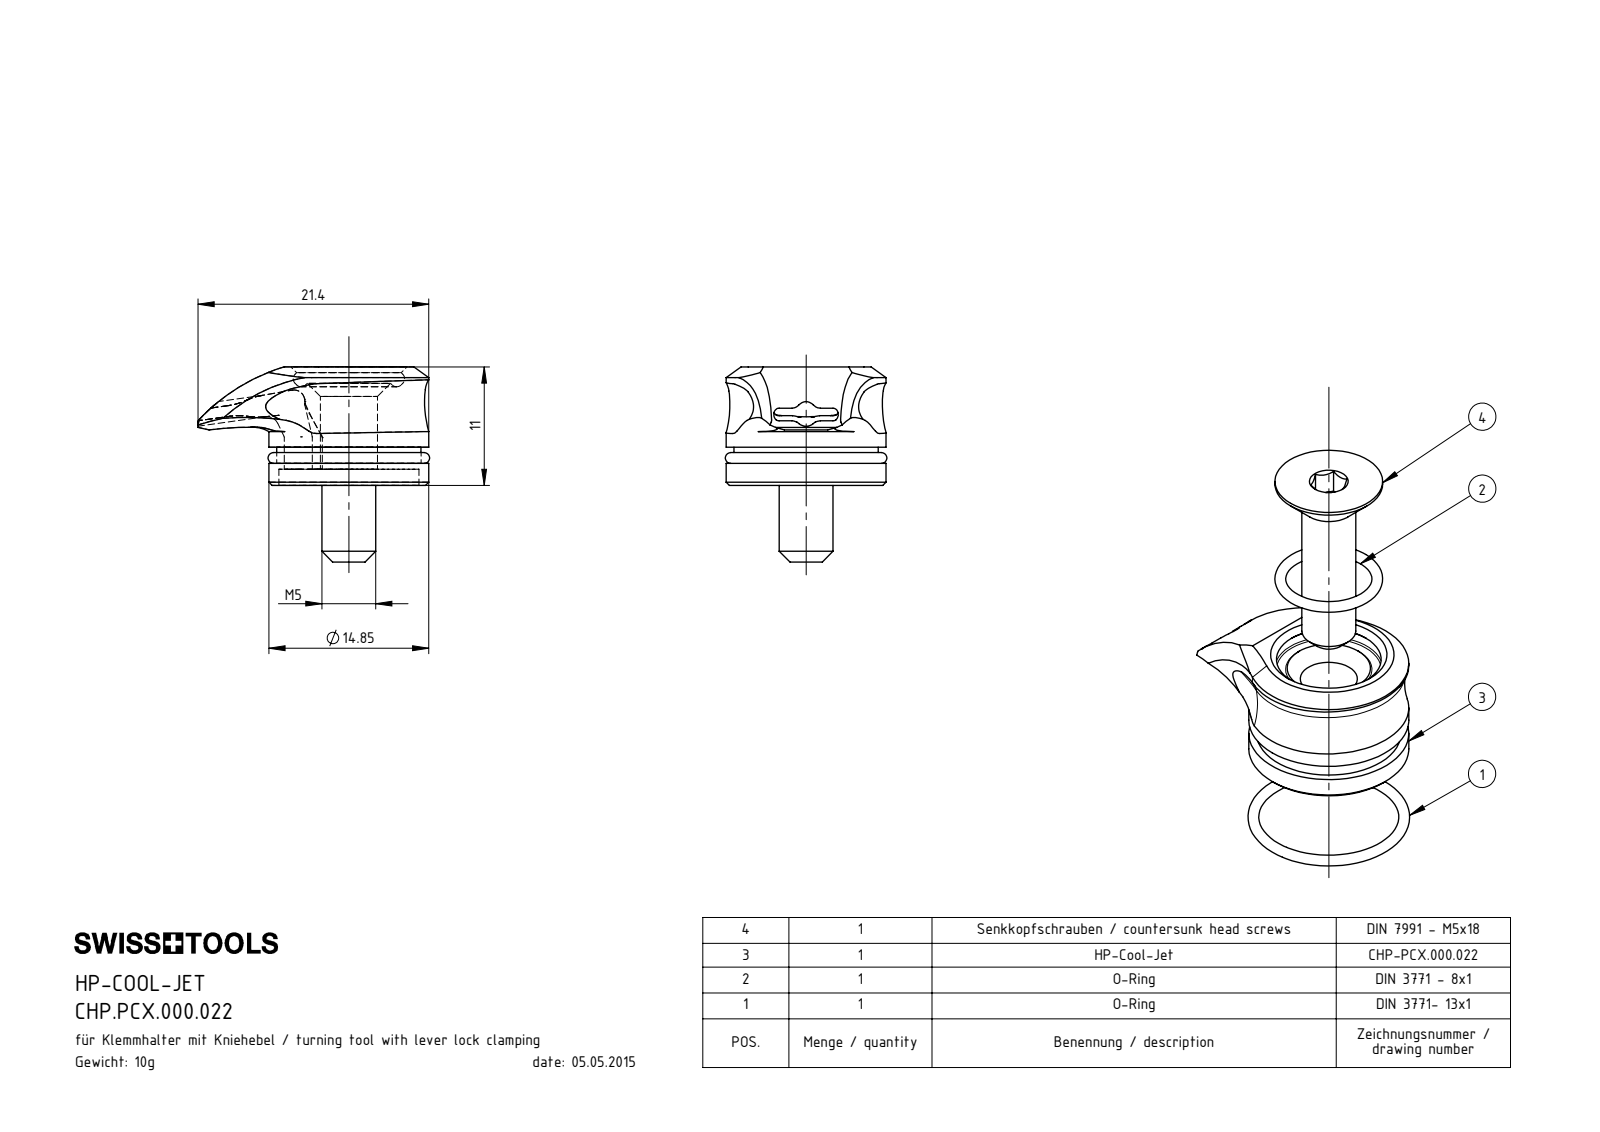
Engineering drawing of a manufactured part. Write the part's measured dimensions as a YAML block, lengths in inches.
part_name: "CHP-PCX.000.022_B; DIN 7991 - M5x18; DIN 3771 - 6.5x1.5; DIN 3771 - 13x1 (+1 more)"
step_written_by: "SolidWorks 2017 (AUTOMOTIVE_DESIGN)"
units: inches
bodies: {solids: 4, faces: 138, planar: 30, cylindrical: 38, other: 70}
overall_size: [0.846, 0.713, 0.591]
volume: 0.108
surface_area: 3.264
round_holes:
  - {diameter: 0.209, count: 1}
  - {diameter: 0.512, count: 1}
round_bosses_or_shafts:
  - {diameter: 0.585, count: 1}
  - {diameter: 0.528, count: 1}
  - {diameter: 0.394, count: 1}
  - {diameter: 0.197, count: 1}
partial_cylinders:
  - {radius: 0.039, count: 7}
  - {radius: 0.236, count: 3}
  - {radius: 0.02, count: 2}
  - {radius: 0.043, count: 2}
  - {radius: 0.047, count: 2}
  - {radius: 0.197, count: 2}
  - {radius: 0.902, count: 2}
  - {radius: 0.012, count: 1}
face_to_face_distances: [0.37, 0.081, 0.059, 0.289, 0.022, 0.348, 0.374, 0.352, 0.293, 0.14]
